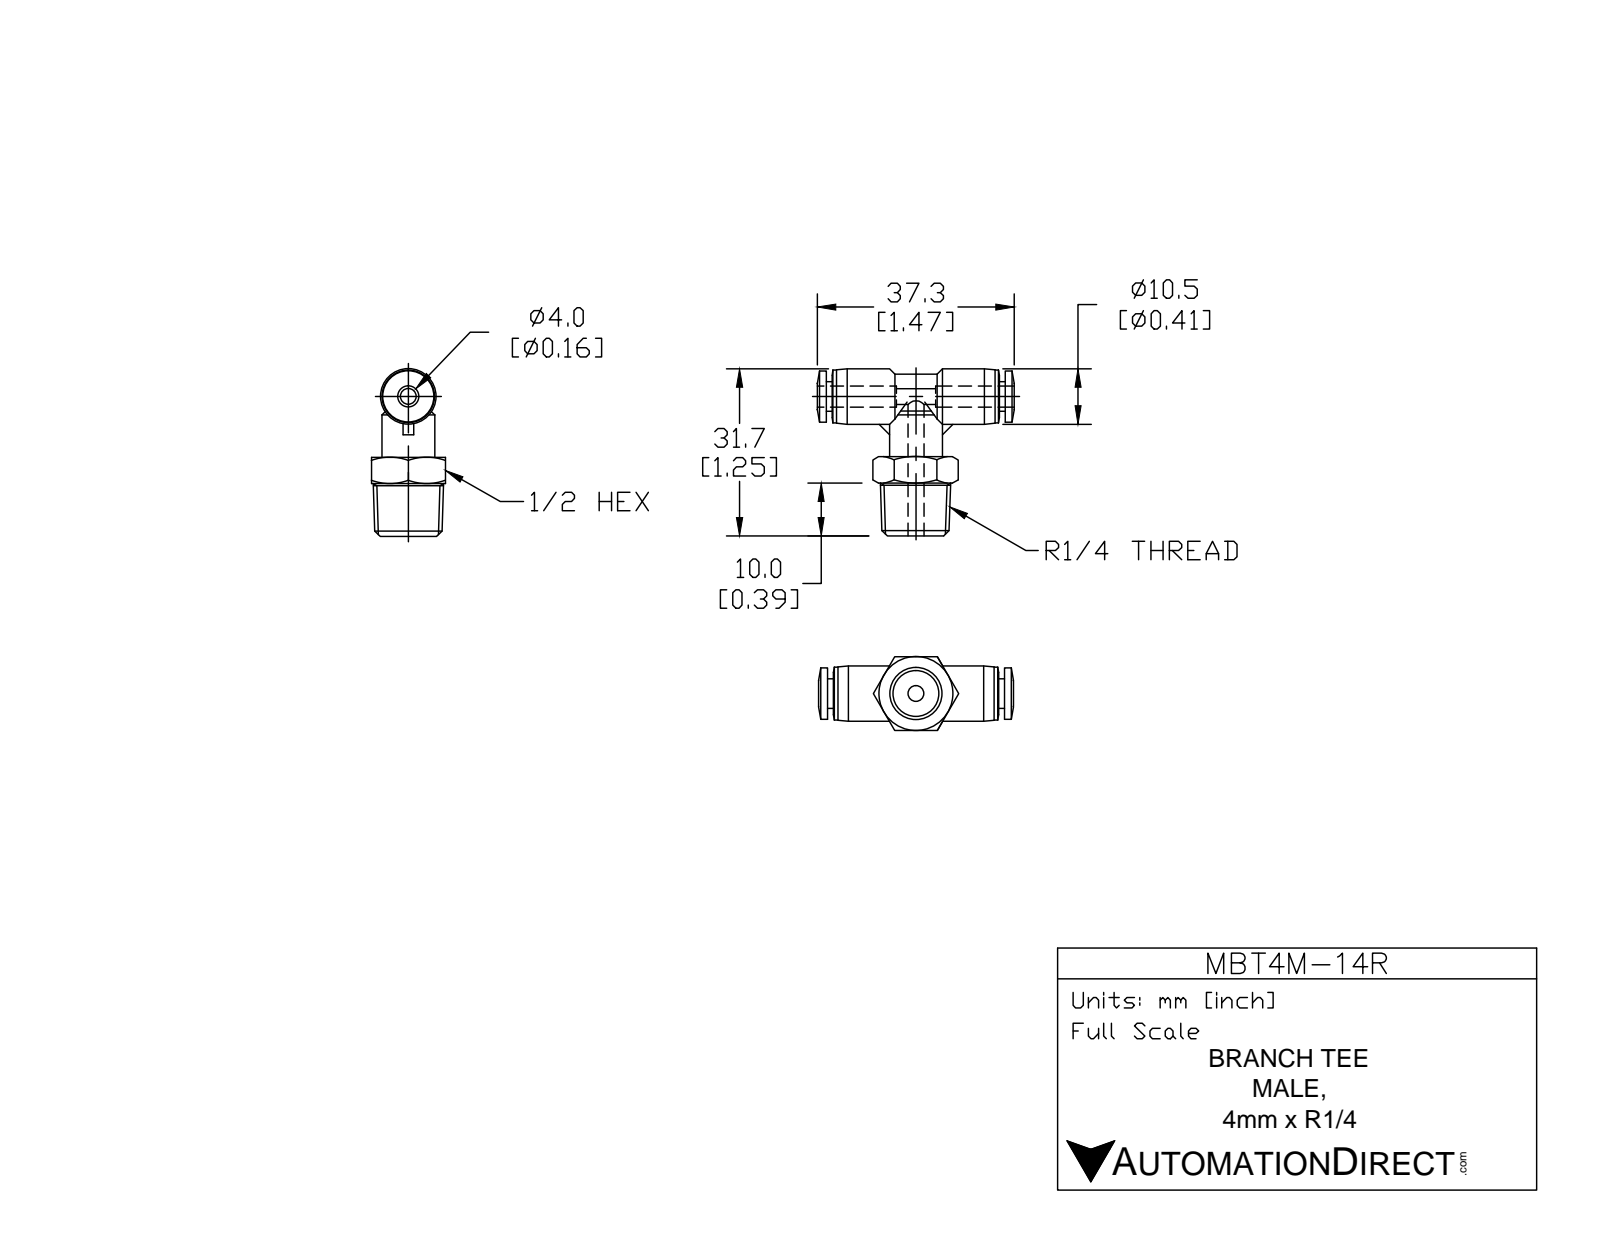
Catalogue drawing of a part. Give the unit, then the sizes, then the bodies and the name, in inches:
Units: inches
Overall size (bounding box): 1.453 × 1.25 × 0.551
Round holes (diameter × count): ⌀0.118 ×2, ⌀0.169 ×1
Round bosses / shafts (diameter × count): ⌀0.394 ×2, ⌀0.413 ×1, ⌀0.382 ×1, ⌀0.315 ×1, ⌀0.22 ×1
Partial cylindrical surfaces — rounded edges, fillets, slot ends (radius × count): R0.157 ×1
Main face-to-face distances: 0.551, 0.591, 0.043, 1.276, 1.319, 1.232, 0.394, 0.197, 0.516, 0.803
Volume: 0.29 in³ · Surface area: 4.958 in²
Bodies: 1 solid, 101 faces (25 planar, 33 cylindrical, 43 other)
Part name (STEP PRODUCT): MBT4M-14R
STEP written by: SolidWorks 2015 (AUTOMOTIVE_DESIGN)
